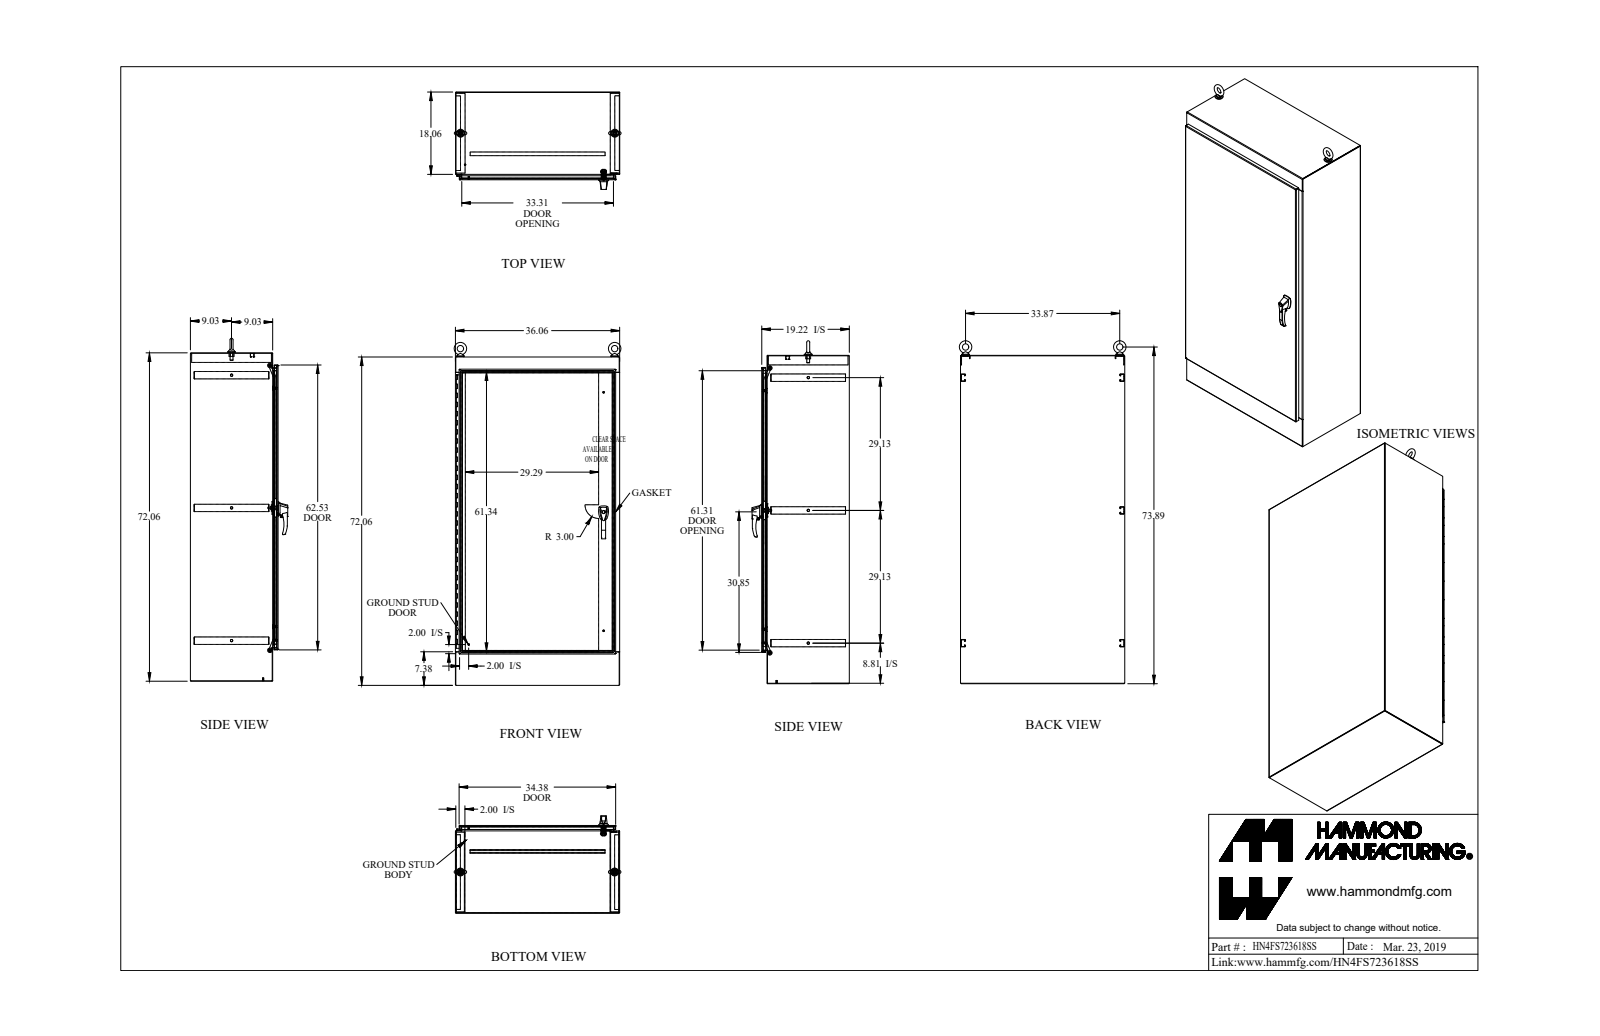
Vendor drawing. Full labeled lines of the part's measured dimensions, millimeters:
Part name (STEP PRODUCT): HN4FS723618SS
STEP written by: SolidWorks 2018 (AUTOMOTIVE_DESIGN)
Units: millimetres
Bodies: 53 solids, 1874 faces (869 planar, 840 cylindrical, 165 other)
Overall size (bounding box): 1917.4 × 929.7 × 542.6
Volume: 16 990 000 mm³ · Surface area: 14 070 000 mm²
Round holes (diameter × count): ⌀7.7 ×10, ⌀8.9 ×7, ⌀12.7 ×6, ⌀6.4 ×2, ⌀6.5 ×2, ⌀7.1 ×2, ⌀7.1 ×2, ⌀8 ×2, ⌀9.9 ×2, ⌀10.5 ×2, ⌀13.4 ×2, ⌀15.9 ×2
Round bosses / shafts (diameter × count): ⌀44.5 ×2, ⌀38.1 ×2, ⌀31.8 ×2, ⌀25.4 ×2, ⌀19.1 ×2, ⌀18.7 ×2, ⌀16 ×2, ⌀15.9 ×2
Partial cylindrical surfaces — rounded edges, fillets, slot ends (radius × count): R1.1 ×42, R3.5 ×36, R12.7 ×23, R3.2 ×22, R0.5 ×16, R1.2 ×15, R1.5 ×15, R3.6 ×15
Main face-to-face distances: 2.4, 486.5, 913.5, 484, 488.9, 911.1, 1827.9, 915.9, 456.3, 30.1
Hole centre spacings: 152.4, 304.8, 739.9, 457.2, 609.6, 762, 914.4, 1479.8
